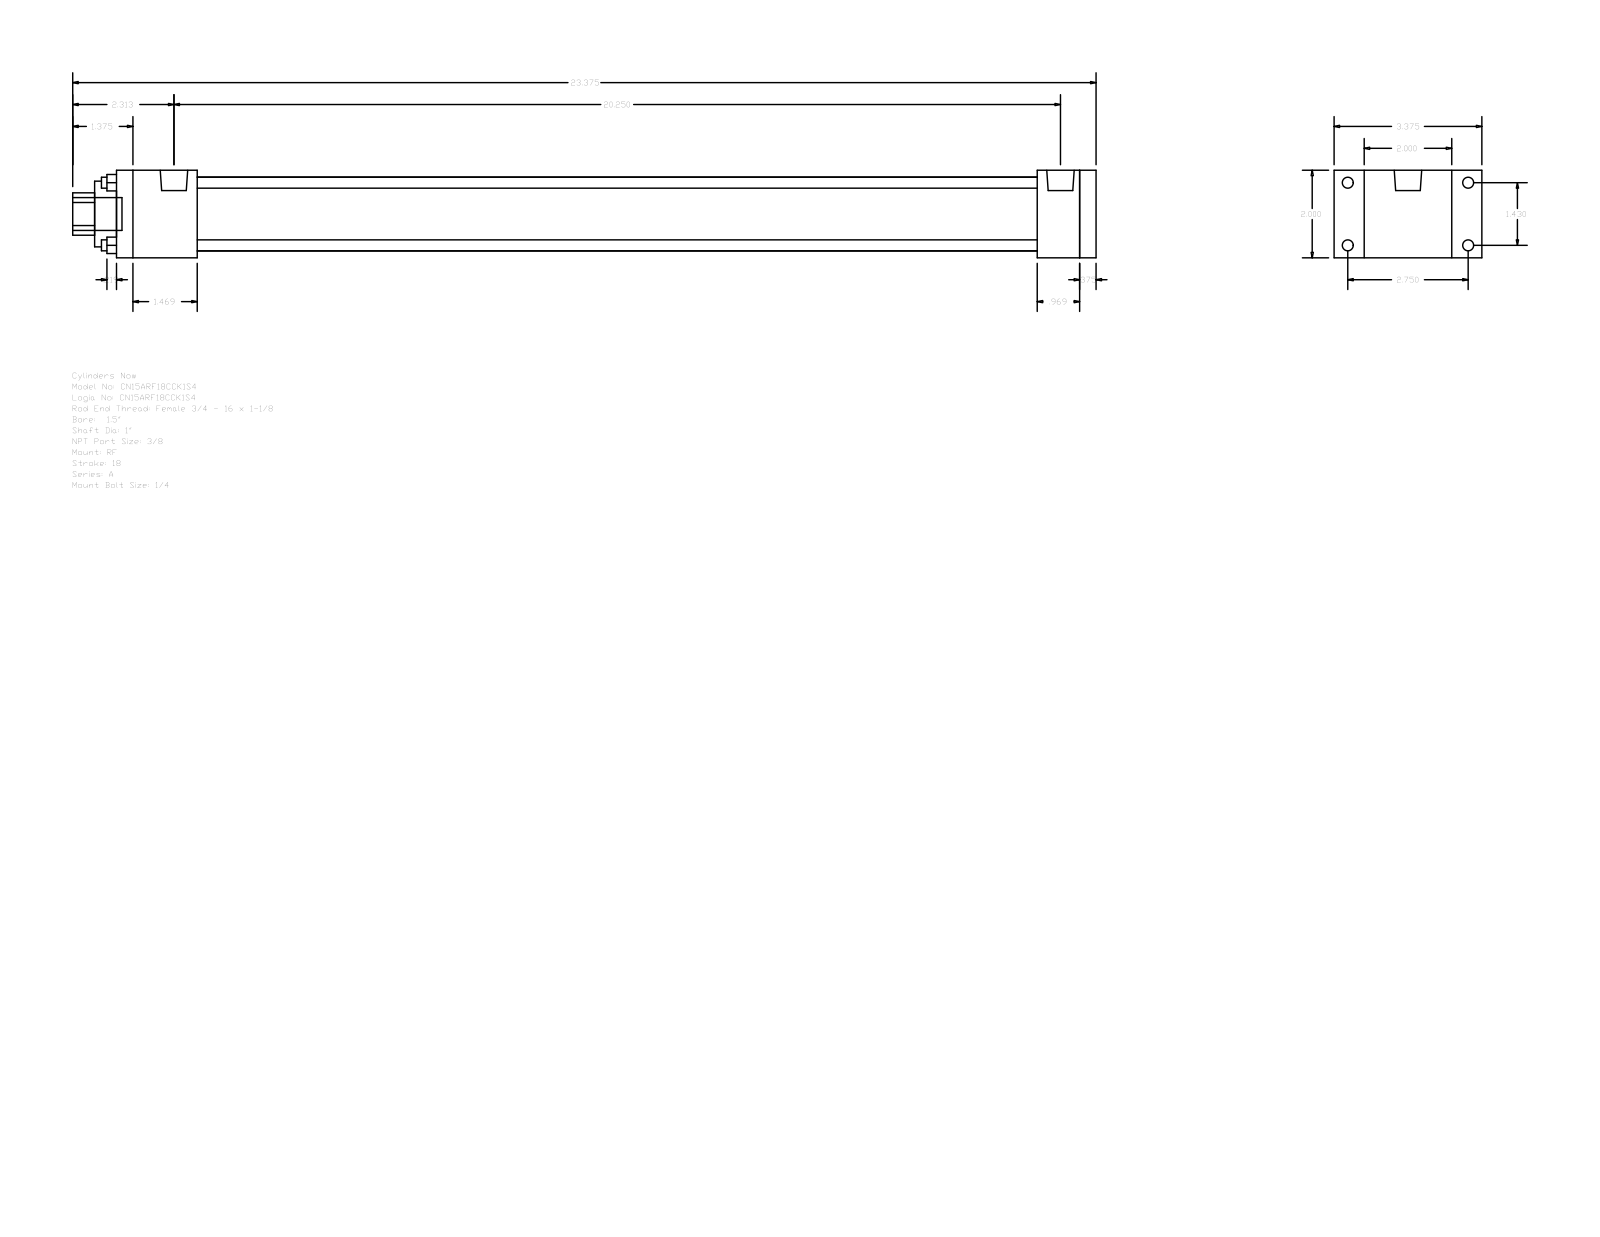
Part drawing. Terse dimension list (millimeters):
name: A_RF__0150_1
written by: GSSL Pune (CONFIG_CONTROL_DESIGN)
unit: mm
bodies: 0 solids, 92 faces (64 planar, 28 cylindrical, 0 other)
size: 593.73 × 85.72 × 50.8
holes: 4× ⌀6.35, 1× ⌀25.4, 1× ⌀38.1, 1× ⌀42.93
bosses: 4× ⌀6.35, 4× ⌀5.56, 2× ⌀15.93, 1× ⌀19.05
rounds: 1× R12.29
face distances: 50.8, 9.53, 558.8, 568.33, 534.19, 24.61, 34.14, 46.83, 487.36, 511.97
hole spacings: 25.68, 36.32, 51.36
